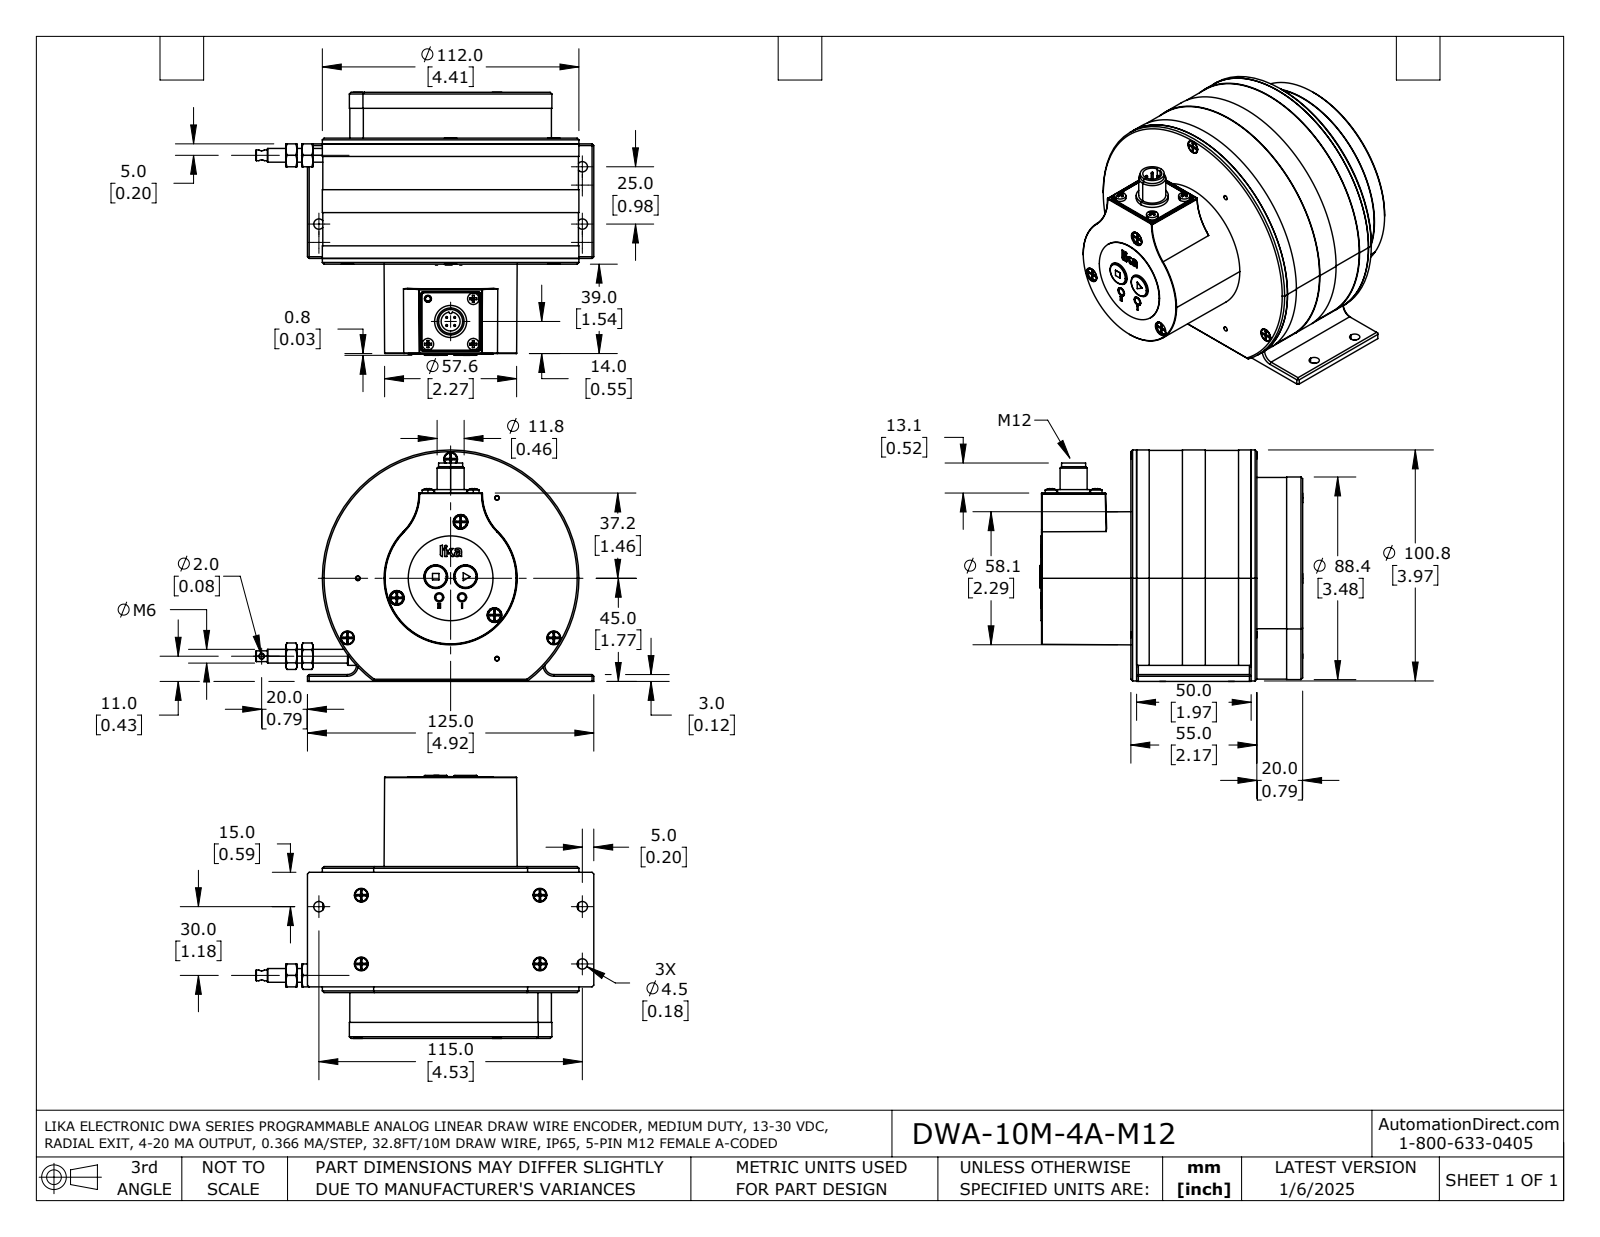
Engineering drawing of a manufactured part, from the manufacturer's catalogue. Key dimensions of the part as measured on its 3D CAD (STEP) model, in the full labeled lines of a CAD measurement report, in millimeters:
Part name (STEP PRODUCT): DWA-10M-4A-M12
STEP written by: SolidWorks 2021 (AUTOMOTIVE_DESIGN)
Units: millimetres
Bodies: 34 solids, 2254 faces (1254 planar, 476 cylindrical, 524 other)
Overall size (bounding box): 147.5 × 114.8 × 101
Volume: 273 500 mm³ · Surface area: 147 700 mm²
Round holes (diameter × count): ⌀2.5 ×13, ⌀3.2 ×7, ⌀6 ×7, ⌀4 ×4, ⌀4.5 ×4, ⌀5 ×4, ⌀2.1 ×3, ⌀2.8 ×3, ⌀1.5 ×2, ⌀1.6 ×2, ⌀2 ×2, ⌀3 ×2
Round bosses / shafts (diameter × count): ⌀3 ×11, ⌀2.5 ×6, ⌀1.4 ×4, ⌀0.8 ×4, ⌀5 ×3, ⌀4 ×2, ⌀112 ×1, ⌀88.4 ×1
Partial cylindrical surfaces — rounded edges, fillets, slot ends (radius × count): R0.2 ×44, R0.2 ×42, R0.5 ×6, R0.8 ×5, R4 ×2, R0.9 ×1, R0.9 ×1, R0.9 ×1
Main face-to-face distances: 2, 20, 0.5, 2.5, 20.5, 52.5, 75, 1.5, 54.5, 55
Hole centre spacings: 25, 43.3, 16.5, 18.5, 12.9, 26.4, 27.7, 31.1
